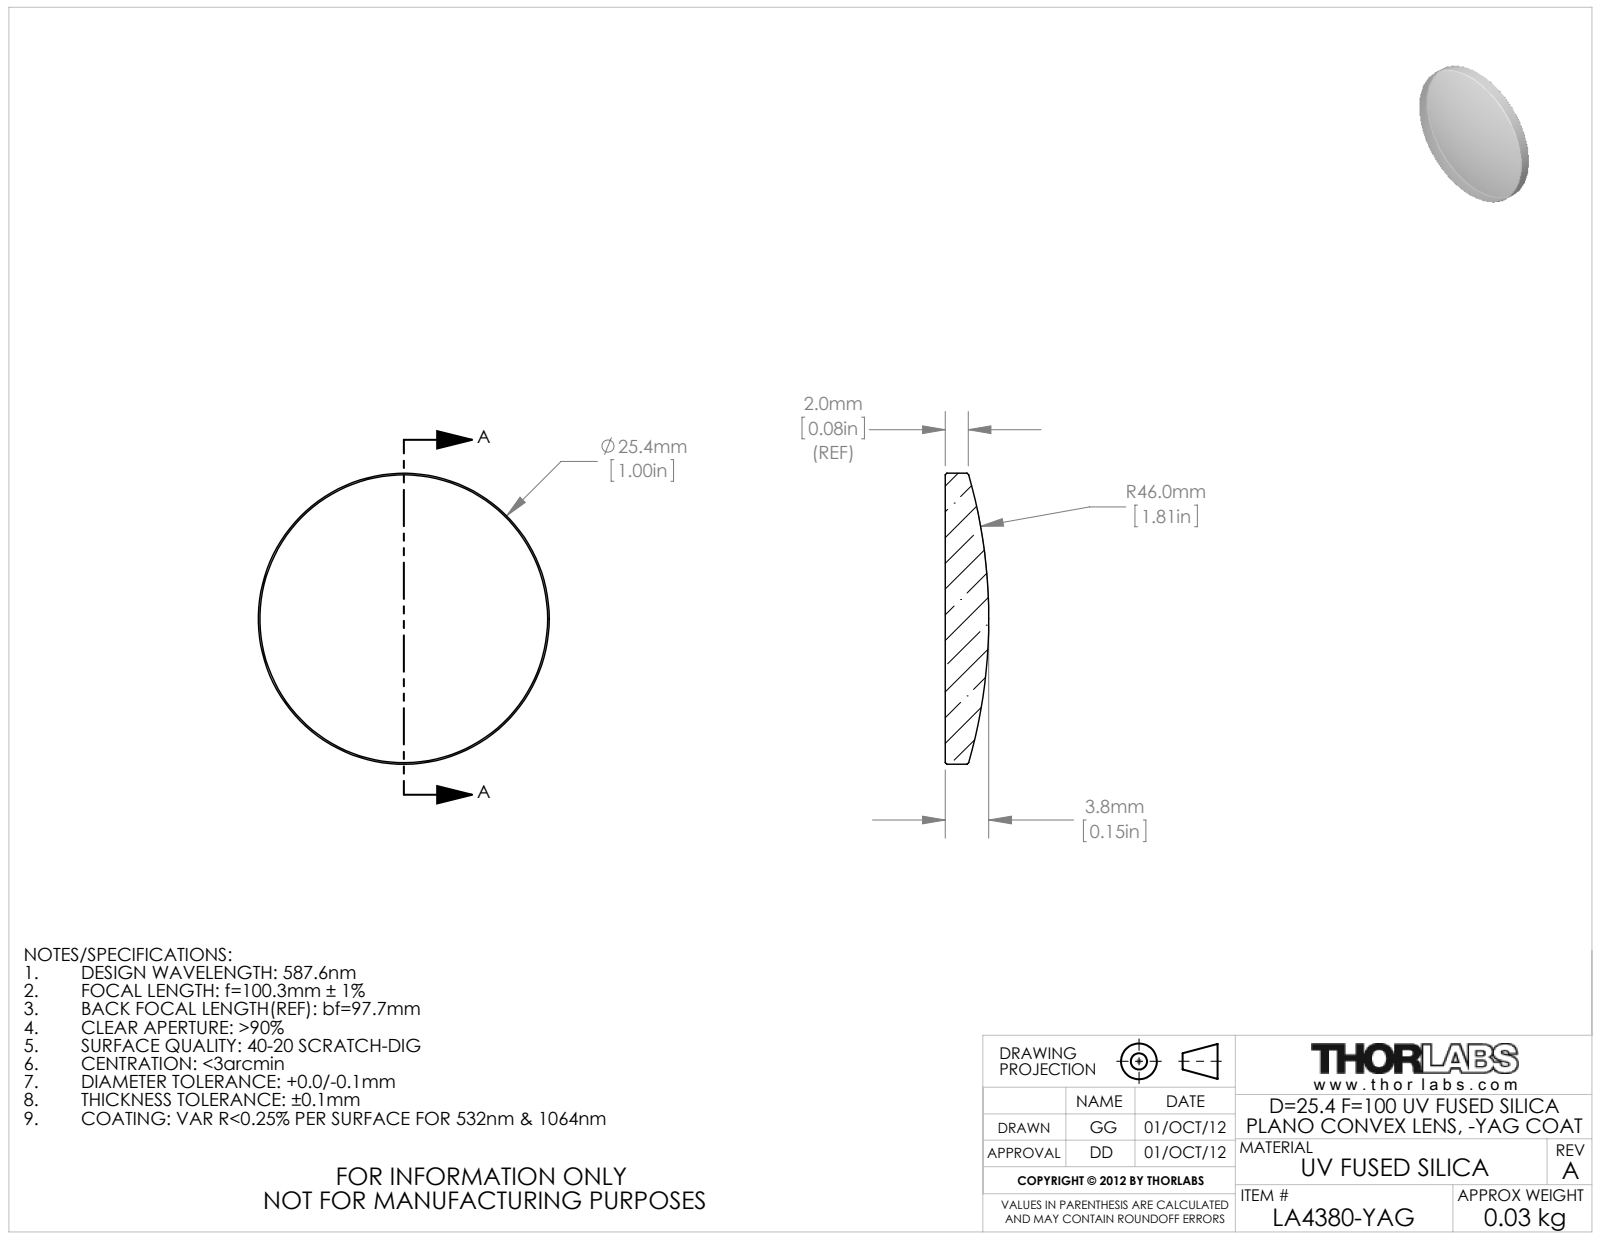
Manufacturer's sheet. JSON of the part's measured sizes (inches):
{"part_name": "24950-E0W", "step_written_by": "SolidWorks 2011 (CONFIG_CONTROL_DESIGN)", "units": "inches", "bodies": {"solids": 1, "faces": 9, "planar": 1, "cylindrical": 2, "other": 6}, "overall_size": [1, 1, 0.149], "volume_in3": 0.09, "surface_area_in2": 1.818, "round_bosses_or_shafts": [[1, 1]]}
